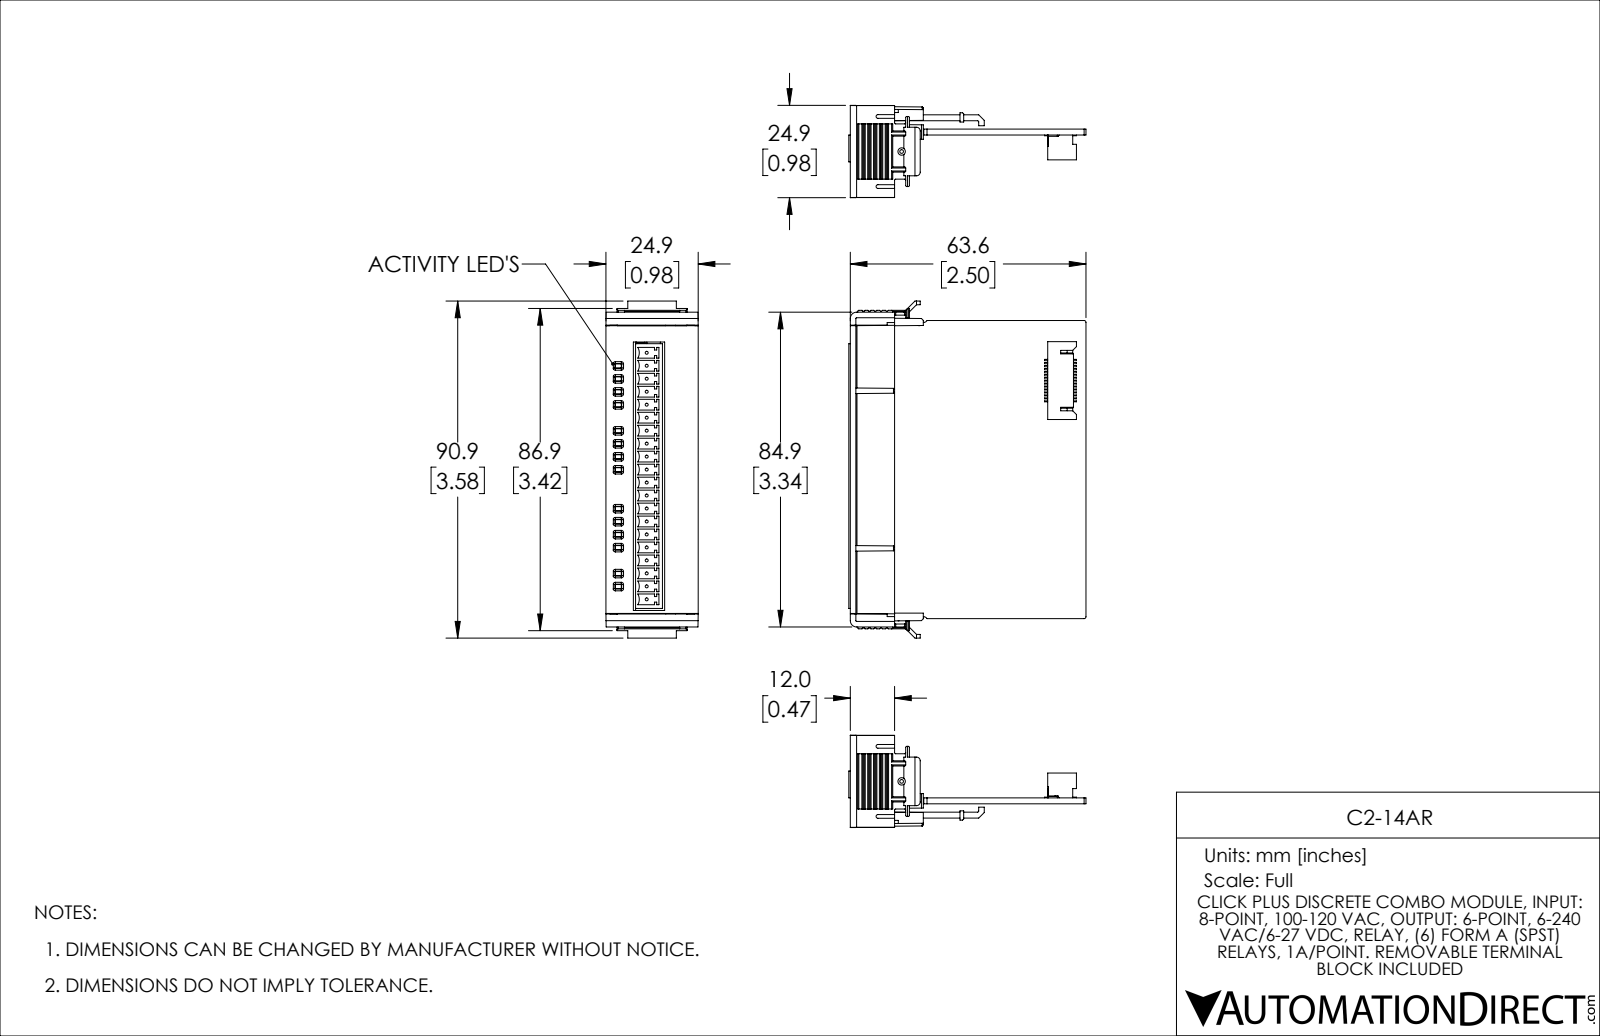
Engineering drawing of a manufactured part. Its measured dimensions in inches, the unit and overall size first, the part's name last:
Units: inches
Overall size (bounding box): 3.595 × 2.52 × 1.092
Round holes (diameter × count): ⌀0.047 ×20
Round bosses / shafts (diameter × count): ⌀0.031 ×40, ⌀0.024 ×2
Partial cylindrical surfaces — rounded edges, fillets, slot ends (radius × count): R0.012 ×59, R0.004 ×46, R0.111 ×20, R0.039 ×17, R0.02 ×13, R0.008 ×10, R0.016 ×4, R0.008 ×2
Main face-to-face distances: 0.063, 0.063, 0.039, 0.156, 0.067, 0.156, 0.844, 0.219, 0.285, 0.348
Hole centre spacings: 0.138, 0.551, 0.689, 0.413, 1.24, 0.276, 0.827, 1.102
Volume: 1.149 in³ · Surface area: 53.72 in²
Bodies: 7 solids, 2608 faces (2196 planar, 256 cylindrical, 156 other)
Part name (STEP PRODUCT): C2-14D1
STEP written by: SolidWorks 2019 (AUTOMOTIVE_DESIGN)
